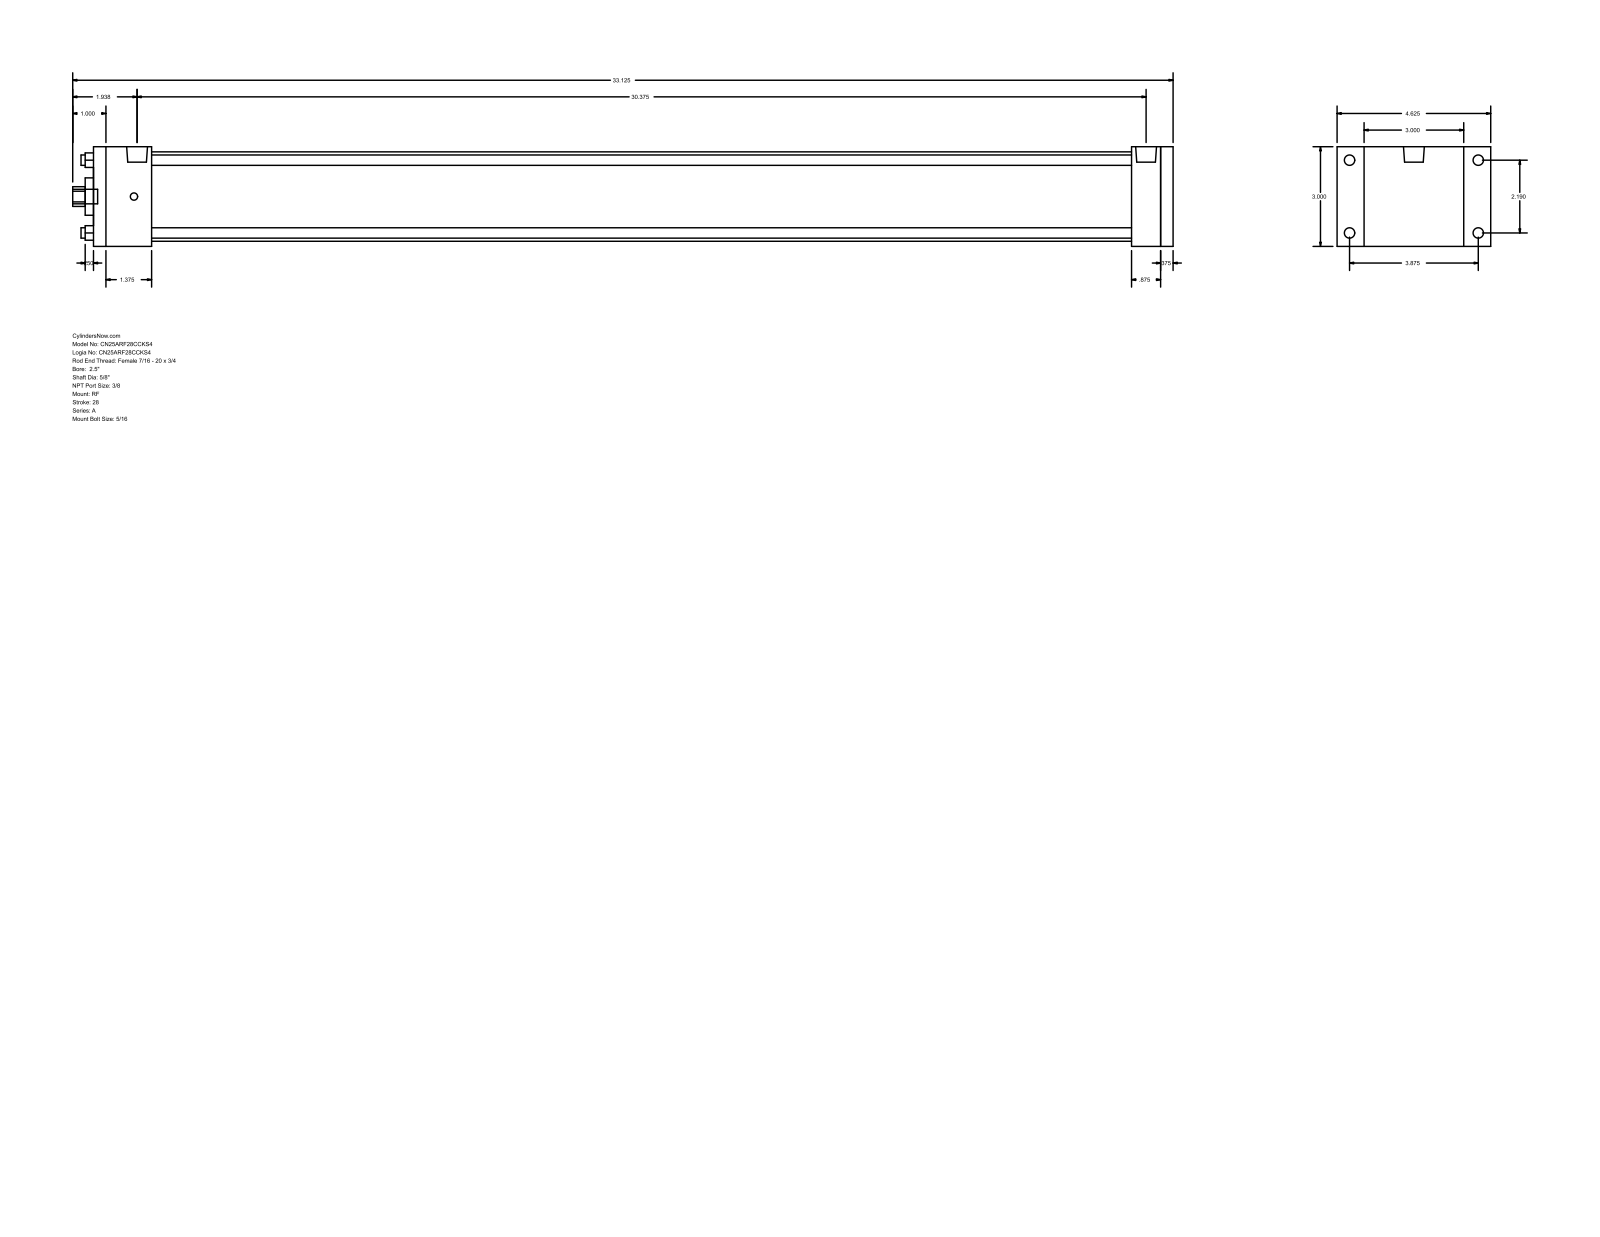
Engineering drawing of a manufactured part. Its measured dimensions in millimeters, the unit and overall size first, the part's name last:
Units: millimetres
Overall size (bounding box): 841.38 × 117.47 × 76.2
Round holes (diameter × count): ⌀7.94 ×4, ⌀15.88 ×1, ⌀28.57 ×1, ⌀68.33 ×1
Round bosses / shafts (diameter × count): ⌀7.94 ×4, ⌀5.56 ×4, ⌀15.93 ×2, ⌀11.11 ×1
Partial cylindrical surfaces — rounded edges, fillets, slot ends (radius × count): R7.54 ×1
Main face-to-face distances: 76.2, 825.5, 9.53, 815.97, 44.45, 793.74, 749.29, 771.52, 781.05, 22.23
Hole centre spacings: 39.33, 55.62, 78.66
Bodies: 0 solids, 92 faces (64 planar, 28 cylindrical, 0 other)
Part name (STEP PRODUCT): A_RF__0250_0.625
STEP written by: GSSL Pune (CONFIG_CONTROL_DESIGN)
